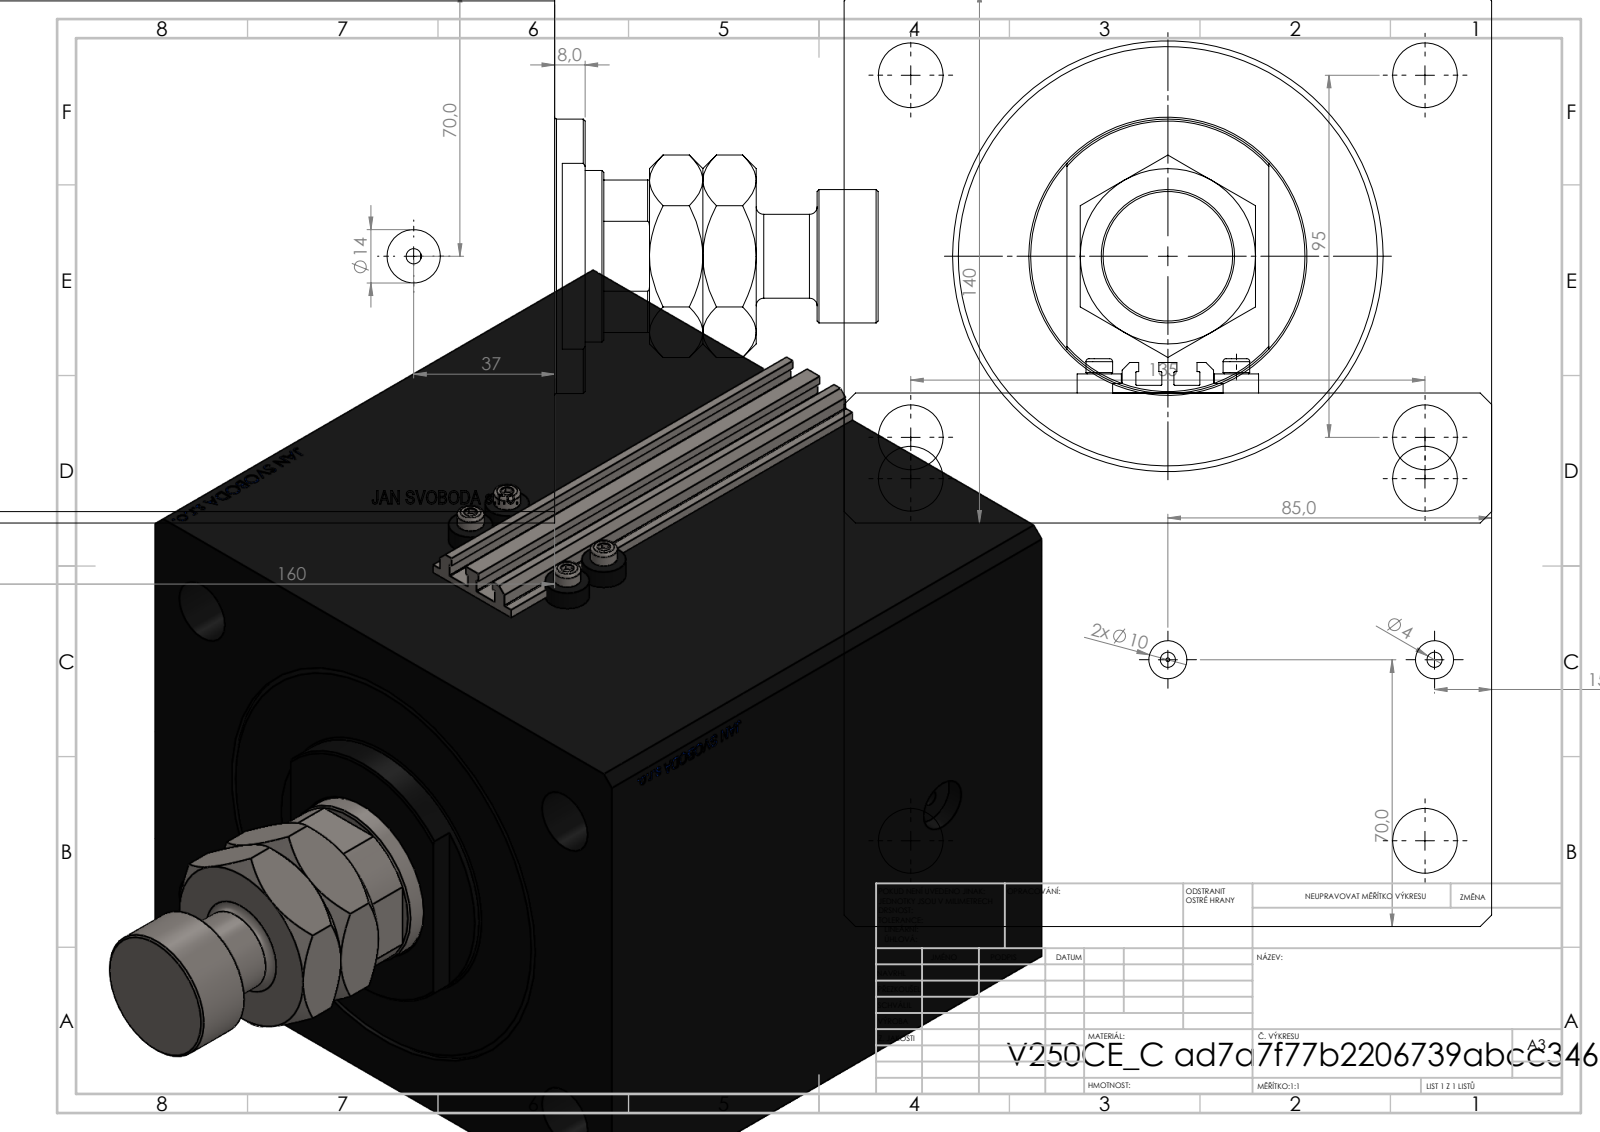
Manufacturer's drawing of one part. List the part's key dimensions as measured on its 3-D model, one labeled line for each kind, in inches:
Part name (STEP PRODUCT): MFA; ALLEN BOLT V250CE; V250CE_VC_C; V250CE_C_Body (+1 more)
STEP written by: SolidWorks 2019 (CONFIG_CONTROL_DESIGN)
Units: inches
Bodies: 9 solids, 1090 faces (520 planar, 92 cylindrical, 478 other)
Overall size (bounding box): 9.642 × 6.693 × 5.866
Volume: 210 in³ · Surface area: 524.8 in²
Round holes (diameter × count): ⌀0.157 ×8, ⌀0.669 ×4, ⌀0.394 ×2, ⌀0.551 ×2, ⌀0.049 ×1, ⌀1.24 ×1, ⌀1.772 ×1, ⌀3.937 ×1, ⌀4.449 ×1
Round bosses / shafts (diameter × count): ⌀0.457 ×4, ⌀0.276 ×4, ⌀2.835 ×1, ⌀1.378 ×1, ⌀0.866 ×1
Partial cylindrical surfaces — rounded edges, fillets, slot ends (radius × count): R0.008 ×10, R0.866 ×1
Main face-to-face distances: 5.512, 6.693, 6.299, 1.138, 5.161, 4.917, 3.78, 1.382, 1.811, 1.969
Hole centre spacings: 3.25, 0.535, 1.417, 1.515, 1.873, 3.74, 5.315, 5.727
